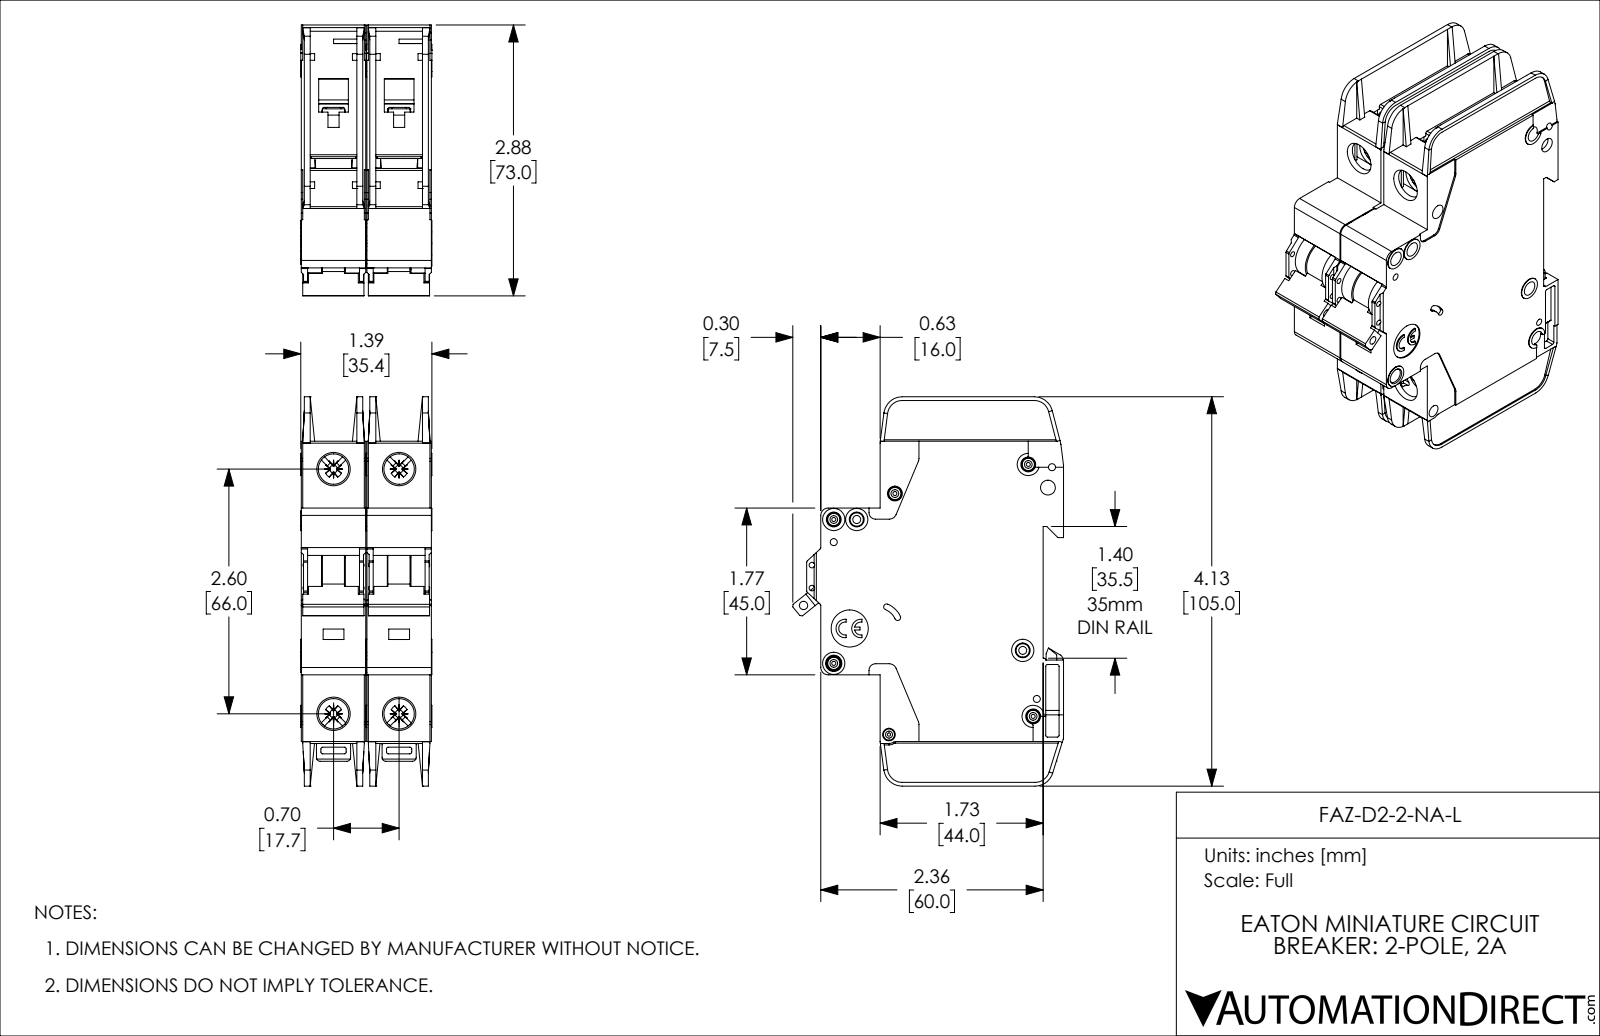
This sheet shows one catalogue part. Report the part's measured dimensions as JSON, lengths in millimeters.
{"part_name": "FAZ-D2-2-NA-L", "step_written_by": "SolidWorks 2019 (AUTOMOTIVE_DESIGN)", "units": "millimeters", "bodies": {"solids": 2, "faces": 2254, "planar": 1342, "cylindrical": 714, "other": 198}, "overall_size": [105, 73.1, 35.4], "volume_mm3": 153500, "surface_area_mm2": 52910, "round_holes": [[4, 8], [1.1, 5], [1.9, 4], [8.2, 4], [1.5, 2], [2.2, 2], [0.9, 1], [2.3, 1], [2.5, 1], [3.4, 1], [10, 1]], "round_bosses_or_shafts": [[3.3, 5], [6, 4], [3, 3], [2.5, 2]], "partial_cylinders_radius": [[0.5, 57], [0.4, 20], [1, 14], [2, 10], [1.1, 8], [0.2, 5], [5, 5], [0.3, 4]], "face_to_face_distances": [17.7, 1.2, 17.4, 15, 2.4, 16.2, 13.8, 35.1, 18.9, 16.5], "hole_center_spacings": [6.2, 13.6, 17.7, 22.1, 66, 68.3, 4.8, 5.1]}
